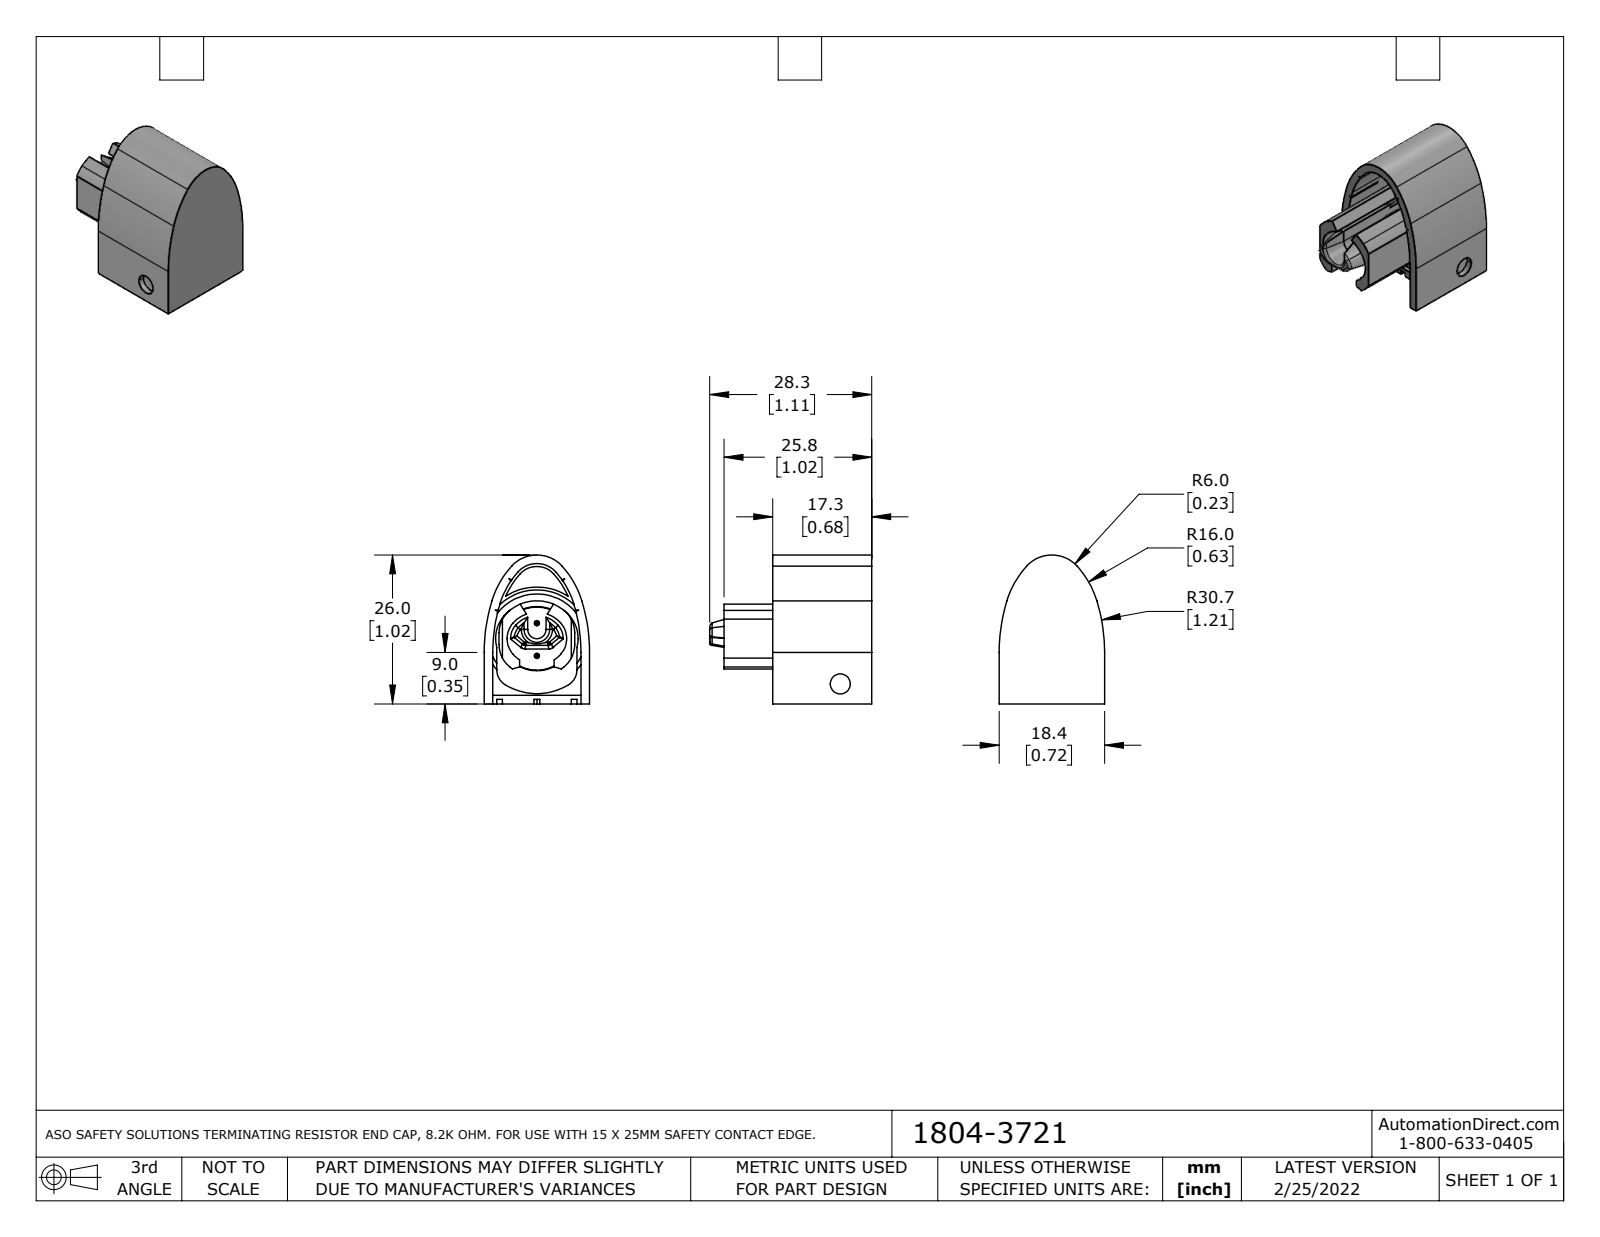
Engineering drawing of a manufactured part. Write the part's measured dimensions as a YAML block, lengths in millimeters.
part_name: "1804-3721_Default"
step_written_by: "SolidWorks 2021 (CONFIG_CONTROL_DESIGN)"
units: millimeters
bodies: {solids: 5, faces: 347, planar: 120, cylindrical: 155, other: 72}
overall_size: [28.3, 26, 18.4]
volume: 4854
surface_area: 6599
round_holes:
  - {diameter: 0.7, count: 2}
  - {diameter: 3.5, count: 2}
  - {diameter: 0.8, count: 1}
round_bosses_or_shafts:
  - {diameter: 1.66, count: 2}
  - {diameter: 0.9, count: 2}
  - {diameter: 0.6, count: 2}
partial_cylinders:
  - {radius: 0.1, count: 8}
  - {radius: 1, count: 8}
  - {radius: 0.5, count: 7}
  - {radius: 0.3, count: 6}
  - {radius: 5, count: 6}
  - {radius: 0.4, count: 2}
  - {radius: 2.9, count: 2}
  - {radius: 3, count: 2}
face_to_face_distances: [1.5, 16.9, 1, 3.2, 1.7, 15.2, 13.7, 8.3, 9.8, 18.4]
hole_center_spacings: [1.5, 5.7]
